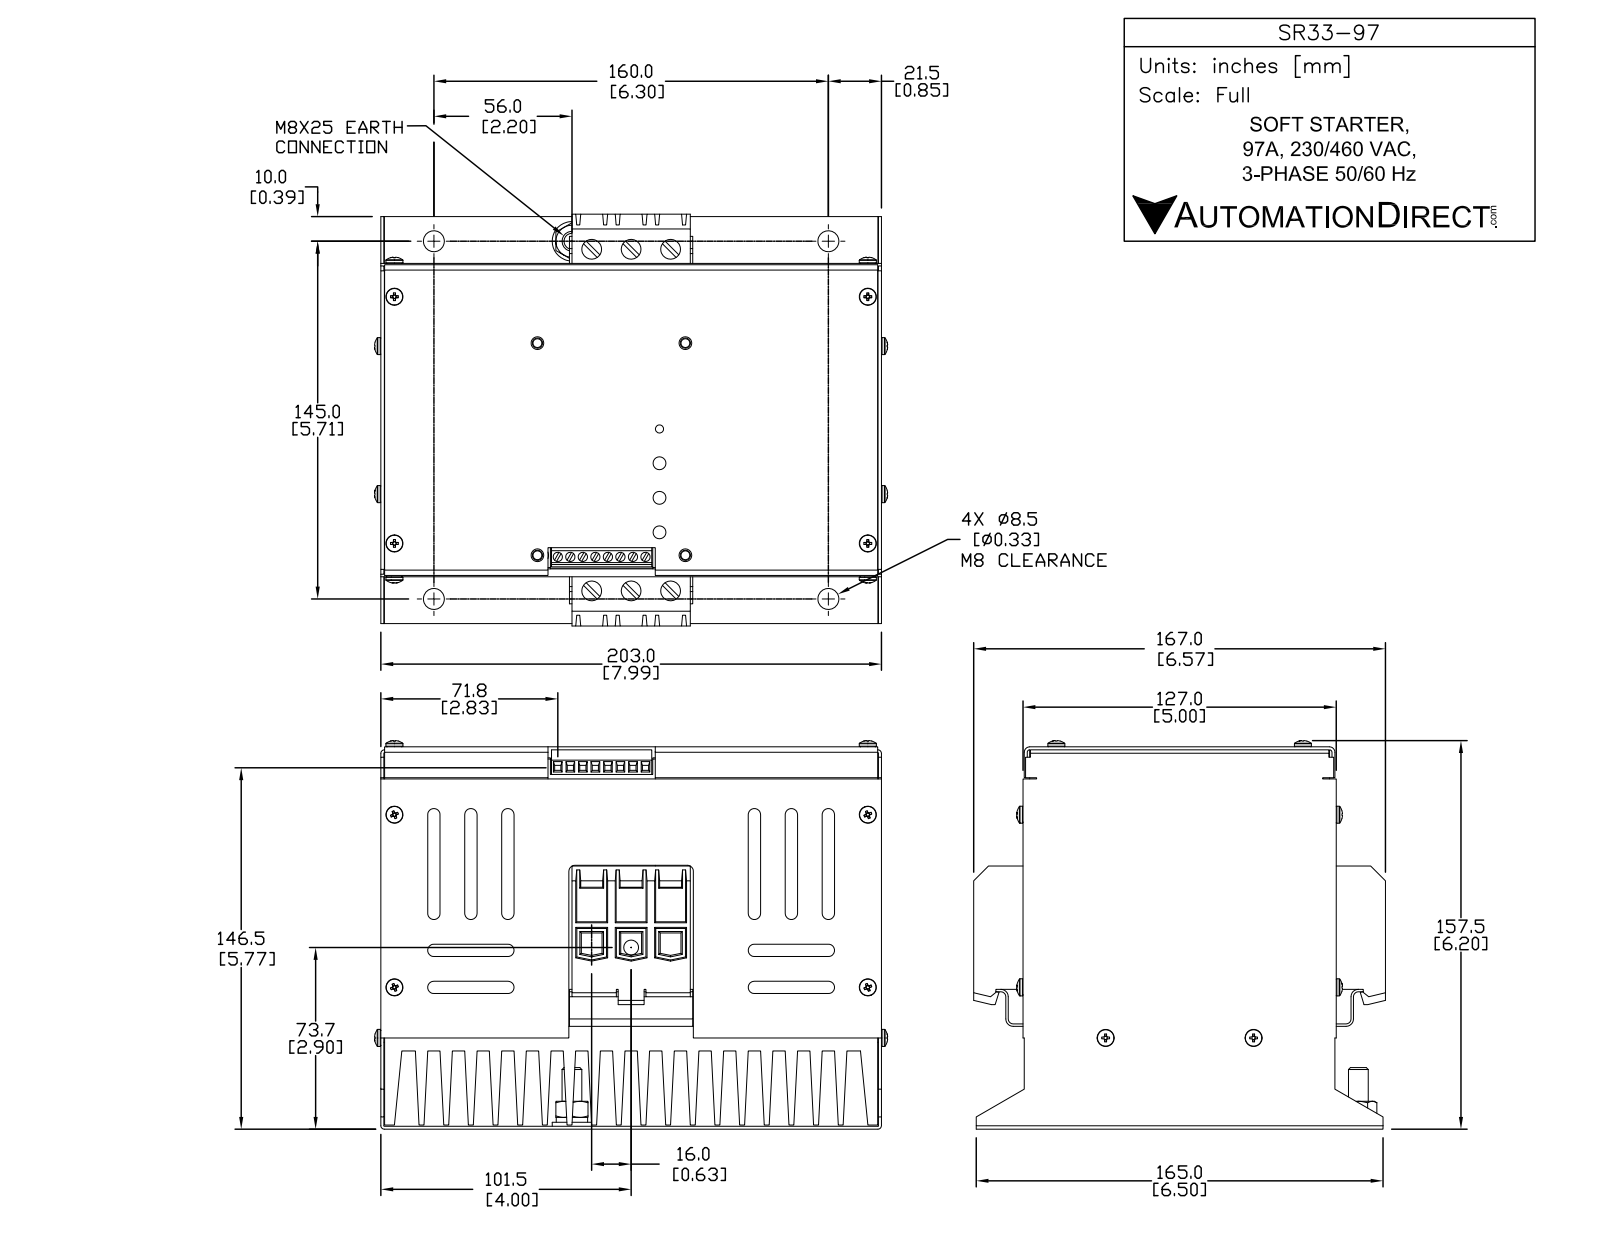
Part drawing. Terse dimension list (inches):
name: SR33-97
written by: SolidWorks 2013 (AUTOMOTIVE_DESIGN)
unit: in
bodies: 1 solid, 838 faces (611 planar, 153 cylindrical, 74 other)
size: 7.992 × 6.496 × 6.22
volume: 201.3 in³; area: 758.8 in²
holes: 8× ⌀0.15, 6× ⌀0.197, 4× ⌀0.335
bosses: 8× ⌀0.272, 1× ⌀0.472, 1× ⌀0.236
rounds: 24× R0.02, 20× R0.098, 8× R0.079, 6× R0.039
face distances: 0.393, 0.787, 1.18, 1.573, 1.967, 2.36, 2.753, 3.146, 3.54, 3.933
hole spacings: 0.194, 0.387, 0.581, 0.591, 0.775, 2.564, 3.154, 3.743
